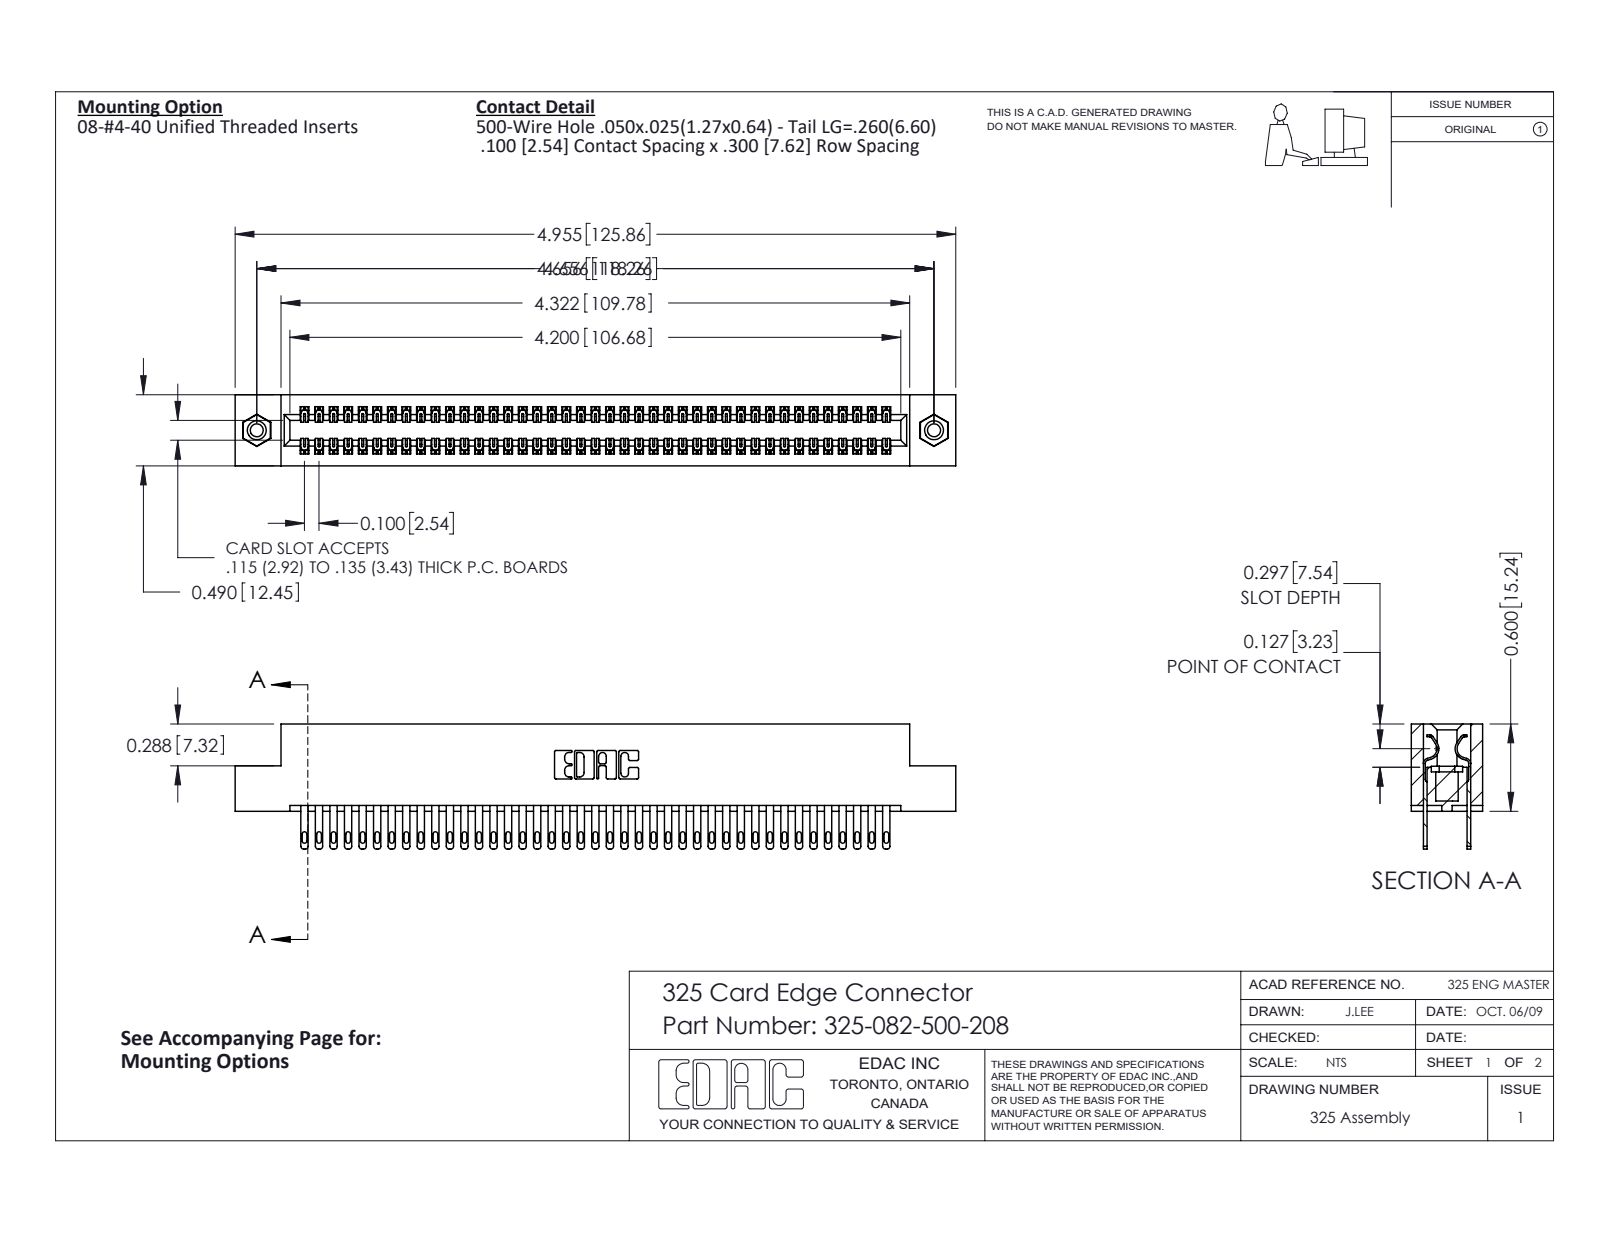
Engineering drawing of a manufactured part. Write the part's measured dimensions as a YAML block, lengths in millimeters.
part_name: "325-082-500-208; 325 Part_TI; 325-292-001_325-293-100; 345-250-001_345-250-003-102"
step_written_by: "SolidWorks 2016 (CONFIG_CONTROL_DESIGN)"
units: millimeters
bodies: {solids: 85, faces: 4110, planar: 2562, cylindrical: 1532, other: 16}
overall_size: [125.9, 21.8, 12.4]
volume: 16490
surface_area: 20800
round_holes:
  - {diameter: 2.3, count: 2}
  - {diameter: 3.2, count: 2}
  - {diameter: 4.1, count: 2}
round_bosses_or_shafts:
  - {diameter: 3.9, count: 2}
partial_cylinders:
  - {radius: 0.2, count: 123}
  - {radius: 0.4, count: 82}
  - {radius: 0.5, count: 82}
  - {radius: 0.3, count: 22}
  - {radius: 0.2, count: 6}
  - {radius: 0.8, count: 6}
  - {radius: 0.7, count: 3}
  - {radius: 0.4, count: 2}
face_to_face_distances: [2.1, 10.3, 7.6, 2.7, 9.7, 0.6, 12.4, 8.3, 7, 14.2]
hole_center_spacings: [118.3]
